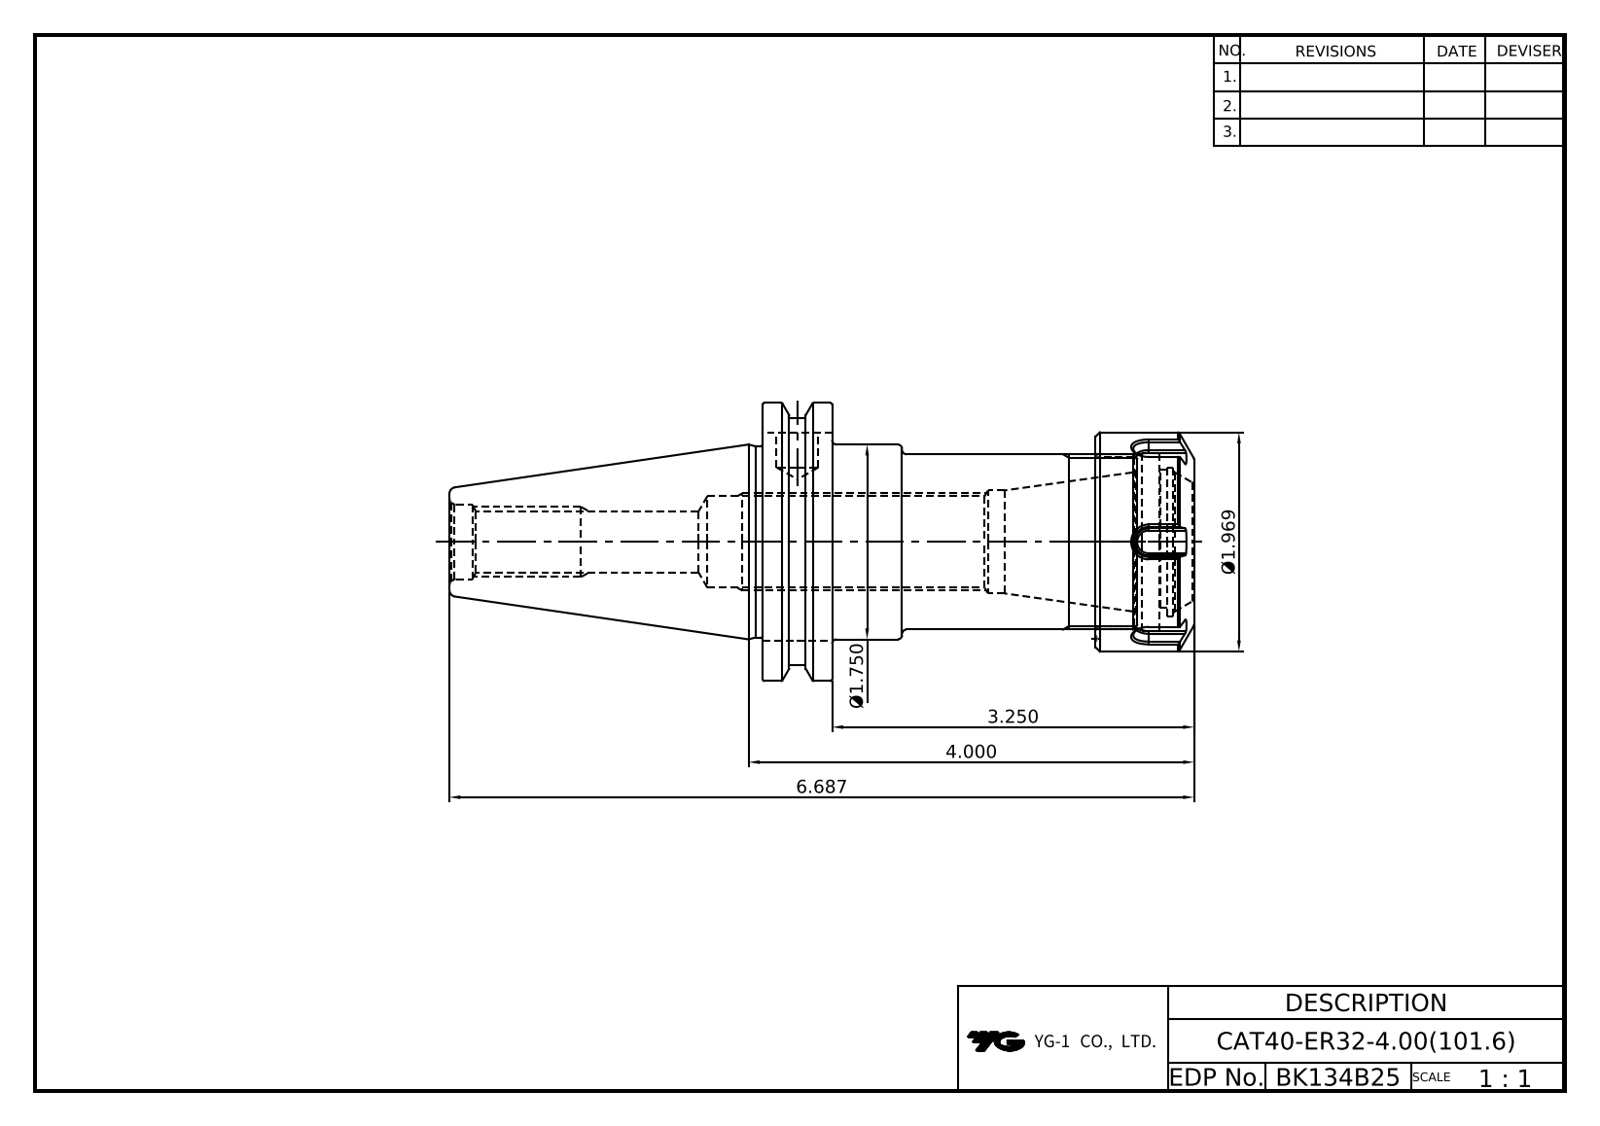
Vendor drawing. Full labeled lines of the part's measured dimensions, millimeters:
Part name (STEP PRODUCT): LO-CAT40-ER32-101.6; ER32NUT
STEP written by: Autodesk Inventor 2025 (AUTOMOTIVE_DESIGN)
Units: millimetres
Bodies: 2 solids, 143 faces (64 planar, 33 cylindrical, 46 other)
Overall size (bounding box): 169.85 × 63.5 × 61.09
Volume: 173 612 mm³ · Surface area: 43 261 mm²
Round holes (diameter × count): ⌀1 ×1, ⌀9.53 ×1, ⌀13.39 ×1, ⌀16.3 ×1, ⌀20.5 ×1, ⌀23.5 ×1, ⌀27.1 ×1, ⌀31.4 ×1, ⌀33.8 ×1, ⌀38.6 ×1, ⌀40.5 ×1
Round bosses / shafts (diameter × count): ⌀63.5 ×1, ⌀56.3 ×1, ⌀50 ×1, ⌀44.45 ×1, ⌀43.6 ×1, ⌀40 ×1
Partial cylindrical surfaces — rounded edges, fillets, slot ends (radius × count): R0.5 ×12
Main face-to-face distances: 15.88, 98.43, 82.55, 75.93, 60.05, 22.5, 90.53, 74.65, 14.6, 7.9
Hole centre spacings: 0.8, 22, 22.8
